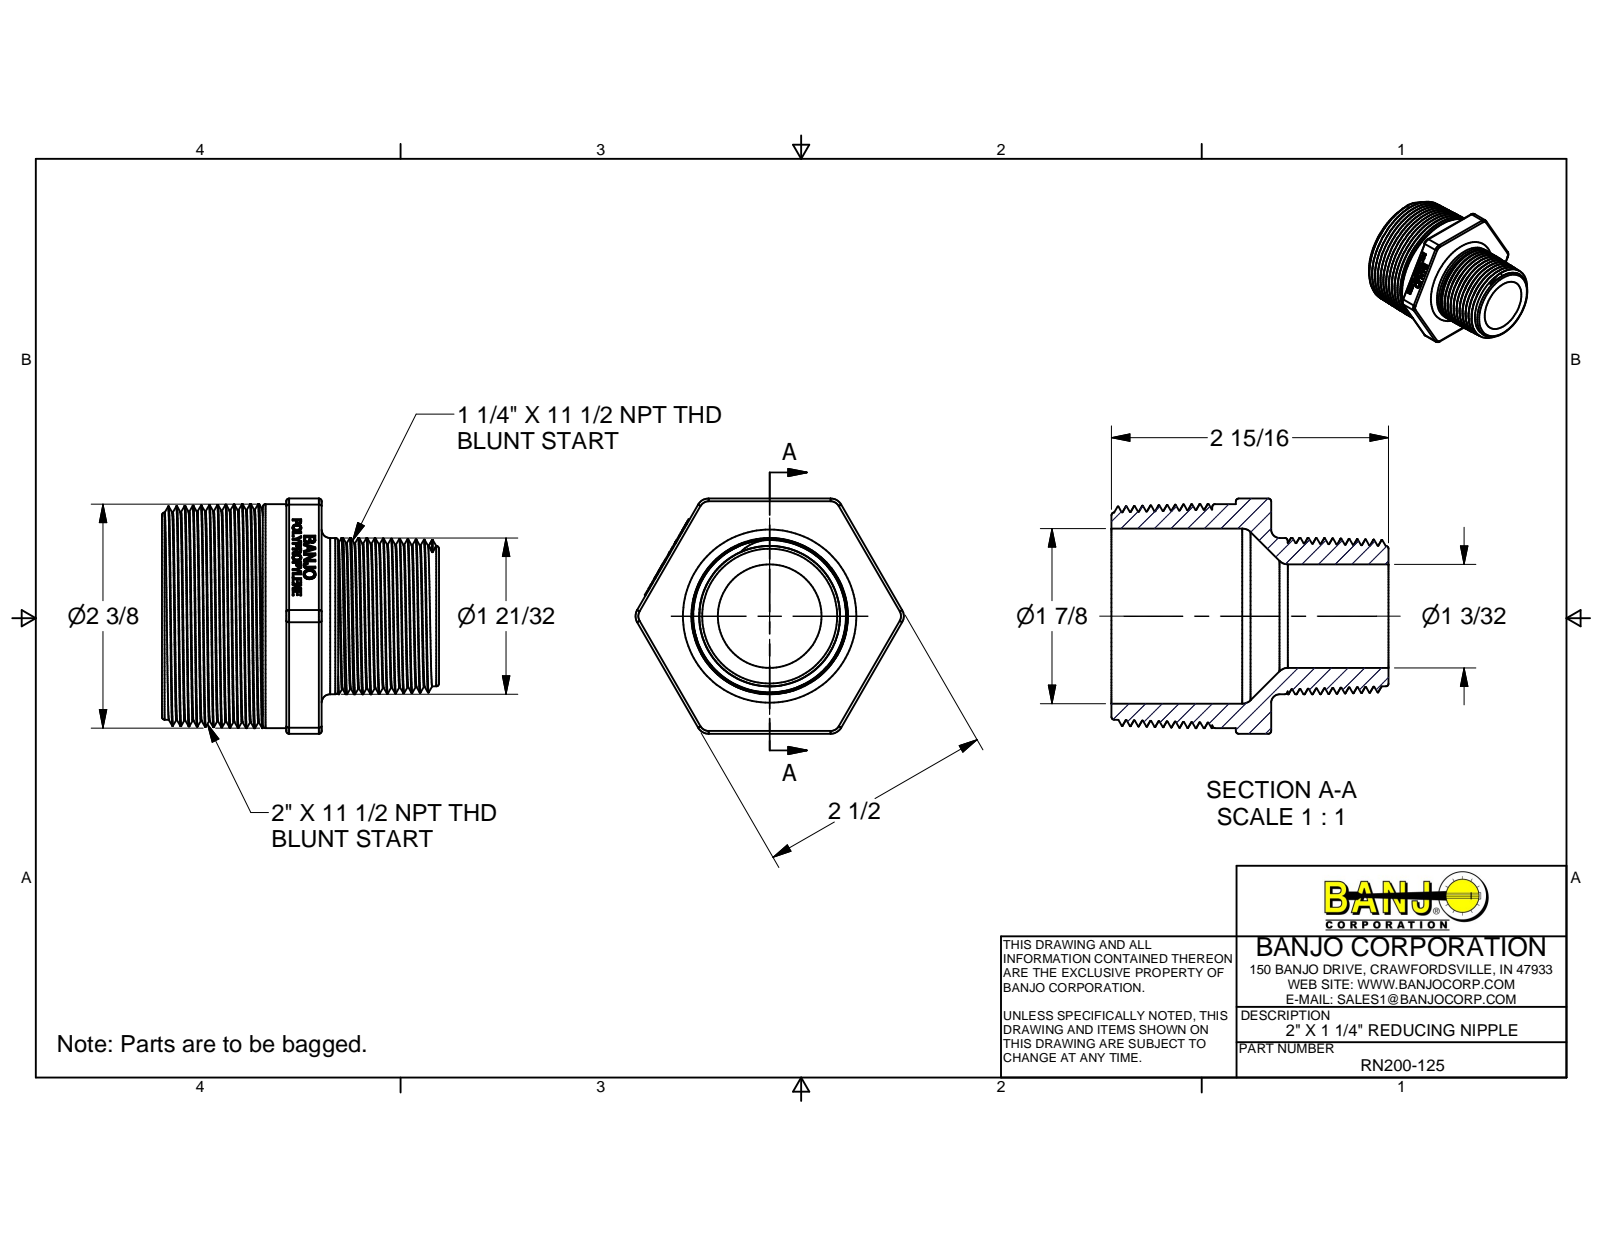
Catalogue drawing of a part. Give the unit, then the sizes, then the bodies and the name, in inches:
Units: inches
Overall size (bounding box): 2.94 × 2.846 × 2.5
Round holes (diameter × count): ⌀1.1 ×1, ⌀1.86 ×1
Round bosses / shafts (diameter × count): ⌀2.38 ×1, ⌀1.66 ×1
Partial cylindrical surfaces — rounded edges, fillets, slot ends (radius × count): R0.03 ×12, R0.13 ×6, R0.436 ×1, R0.614 ×1
Main face-to-face distances: 2.5, 1.695, 1.32, 0.375, 2.94, 1.62, 1.245, 1.07, 1.87, 0.25
Volume: 4.386 in³ · Surface area: 49.72 in²
Bodies: 1 solid, 348 faces (177 planar, 26 cylindrical, 145 other)
Part name (STEP PRODUCT): RN200-125
STEP written by: Autodesk Inventor 2014 (AUTOMOTIVE_DESIGN)
